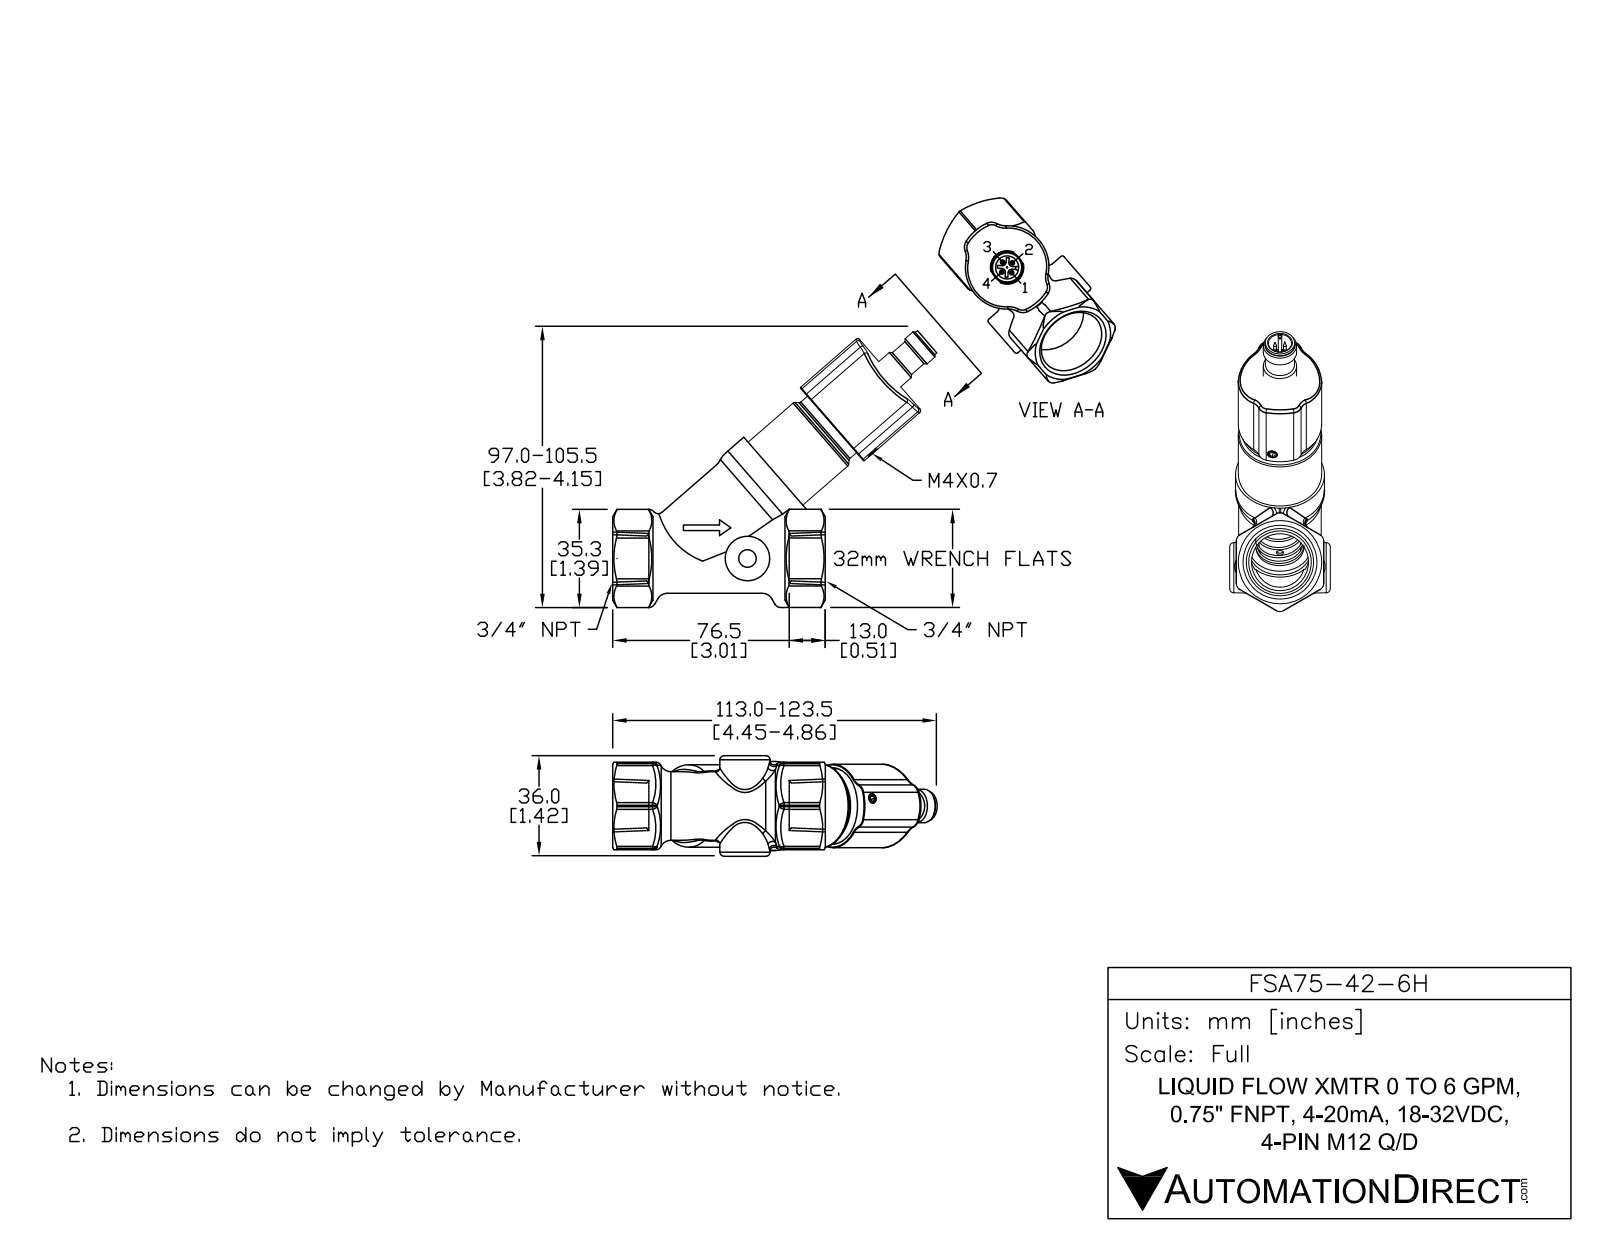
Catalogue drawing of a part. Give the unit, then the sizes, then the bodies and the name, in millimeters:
Units: millimetres
Overall size (bounding box): 116.7 × 100.67 × 36.18
Round holes (diameter × count): ⌀0.5 ×4, ⌀1 ×4, ⌀1.4 ×4, ⌀2.5 ×2, ⌀8.2 ×2, ⌀8.65 ×2, ⌀8.7 ×2, ⌀10.92 ×2, ⌀19 ×2, ⌀3 ×1, ⌀3.24 ×1, ⌀6.2 ×1
Round bosses / shafts (diameter × count): ⌀1.4 ×4, ⌀1 ×4, ⌀0.5 ×4, ⌀16.77 ×2, ⌀31.5 ×1, ⌀30 ×1, ⌀26.9 ×1, ⌀26.4 ×1
Partial cylindrical surfaces — rounded edges, fillets, slot ends (radius × count): R0.45 ×12, R0.2 ×10, R0.8 ×6, R1.2 ×5, R4 ×4, R6 ×4, R2 ×3, R0.55 ×2
Main face-to-face distances: 31.5, 16.25, 1.6, 14.65, 15.25, 16.85, 27.25, 84.67, 8, 40.26
Hole centre spacings: 2.5, 2.51, 2.49, 3.54, 2.48, 2.52, 5
Volume: 74 708 mm³ · Surface area: 54 949 mm²
Bodies: 21 solids, 1179 faces (319 planar, 337 cylindrical, 523 other)
Part name (STEP PRODUCT): FSA75-42-6H
STEP written by: SolidWorks 2017 (AUTOMOTIVE_DESIGN)
